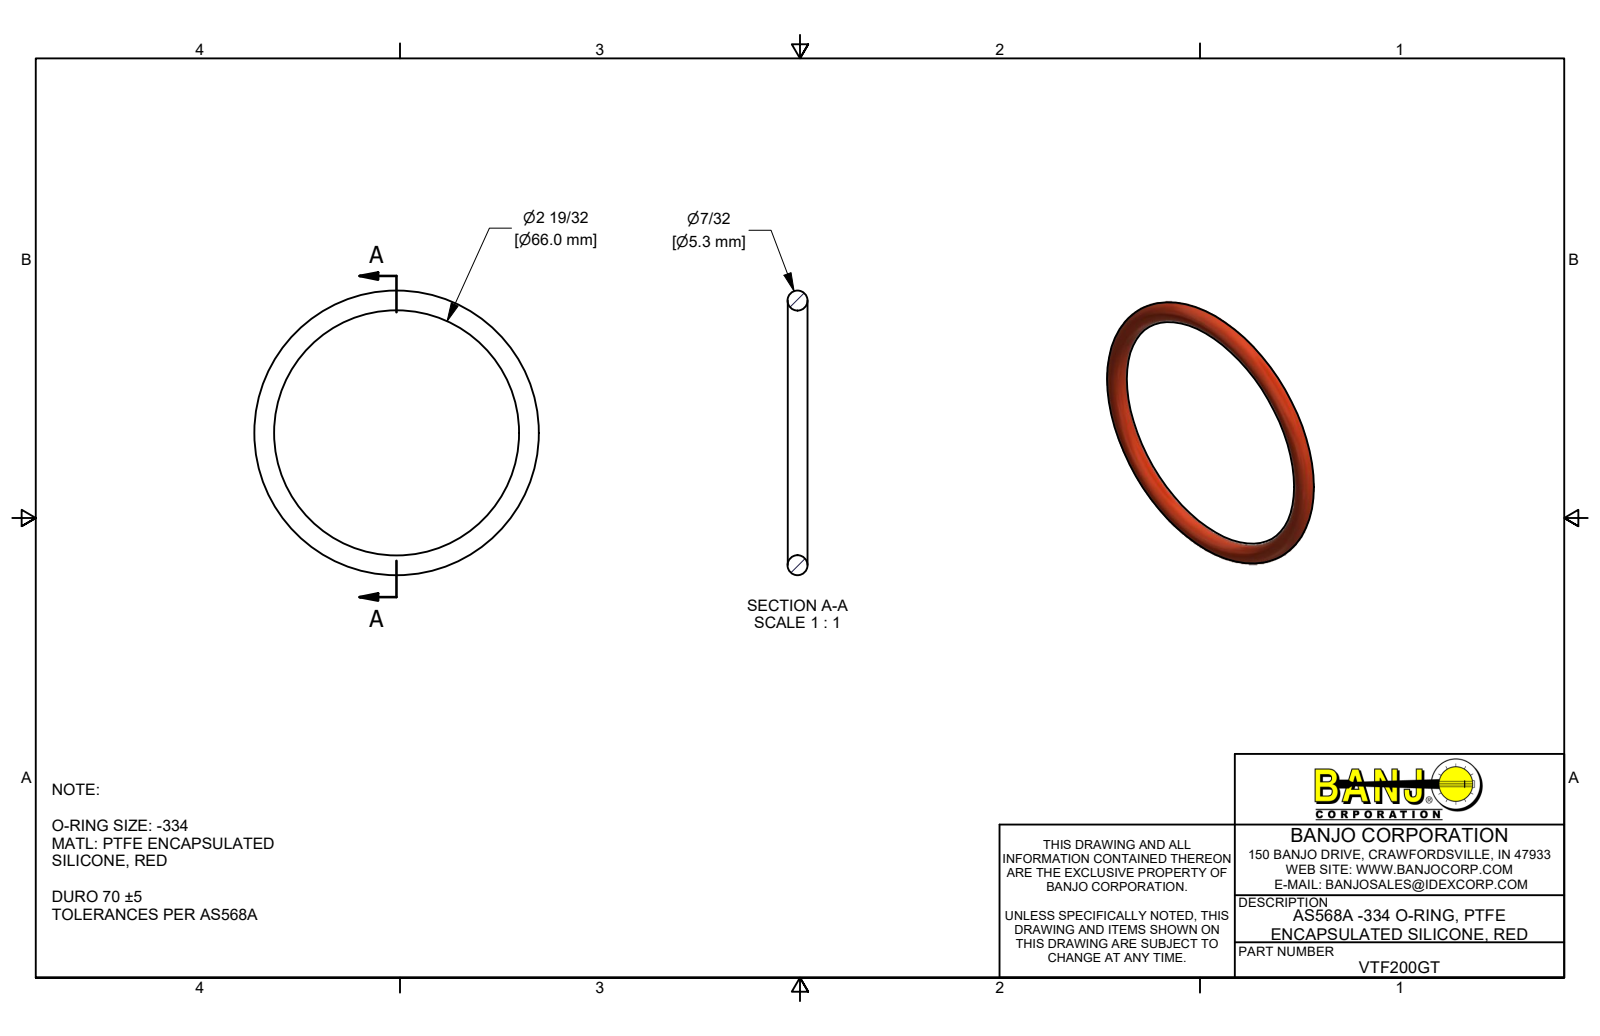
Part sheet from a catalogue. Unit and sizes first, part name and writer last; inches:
Units: inches
Overall size (bounding box): 3.02 × 3.02 × 0.21
Volume: 0.306 in³ · Surface area: 5.824 in²
Bodies: 1 solid, 1 faces (0 planar, 0 cylindrical, 1 other)
Part name (STEP PRODUCT): VTF200GT
STEP written by: Autodesk Inventor 2019 (AUTOMOTIVE_DESIGN)
